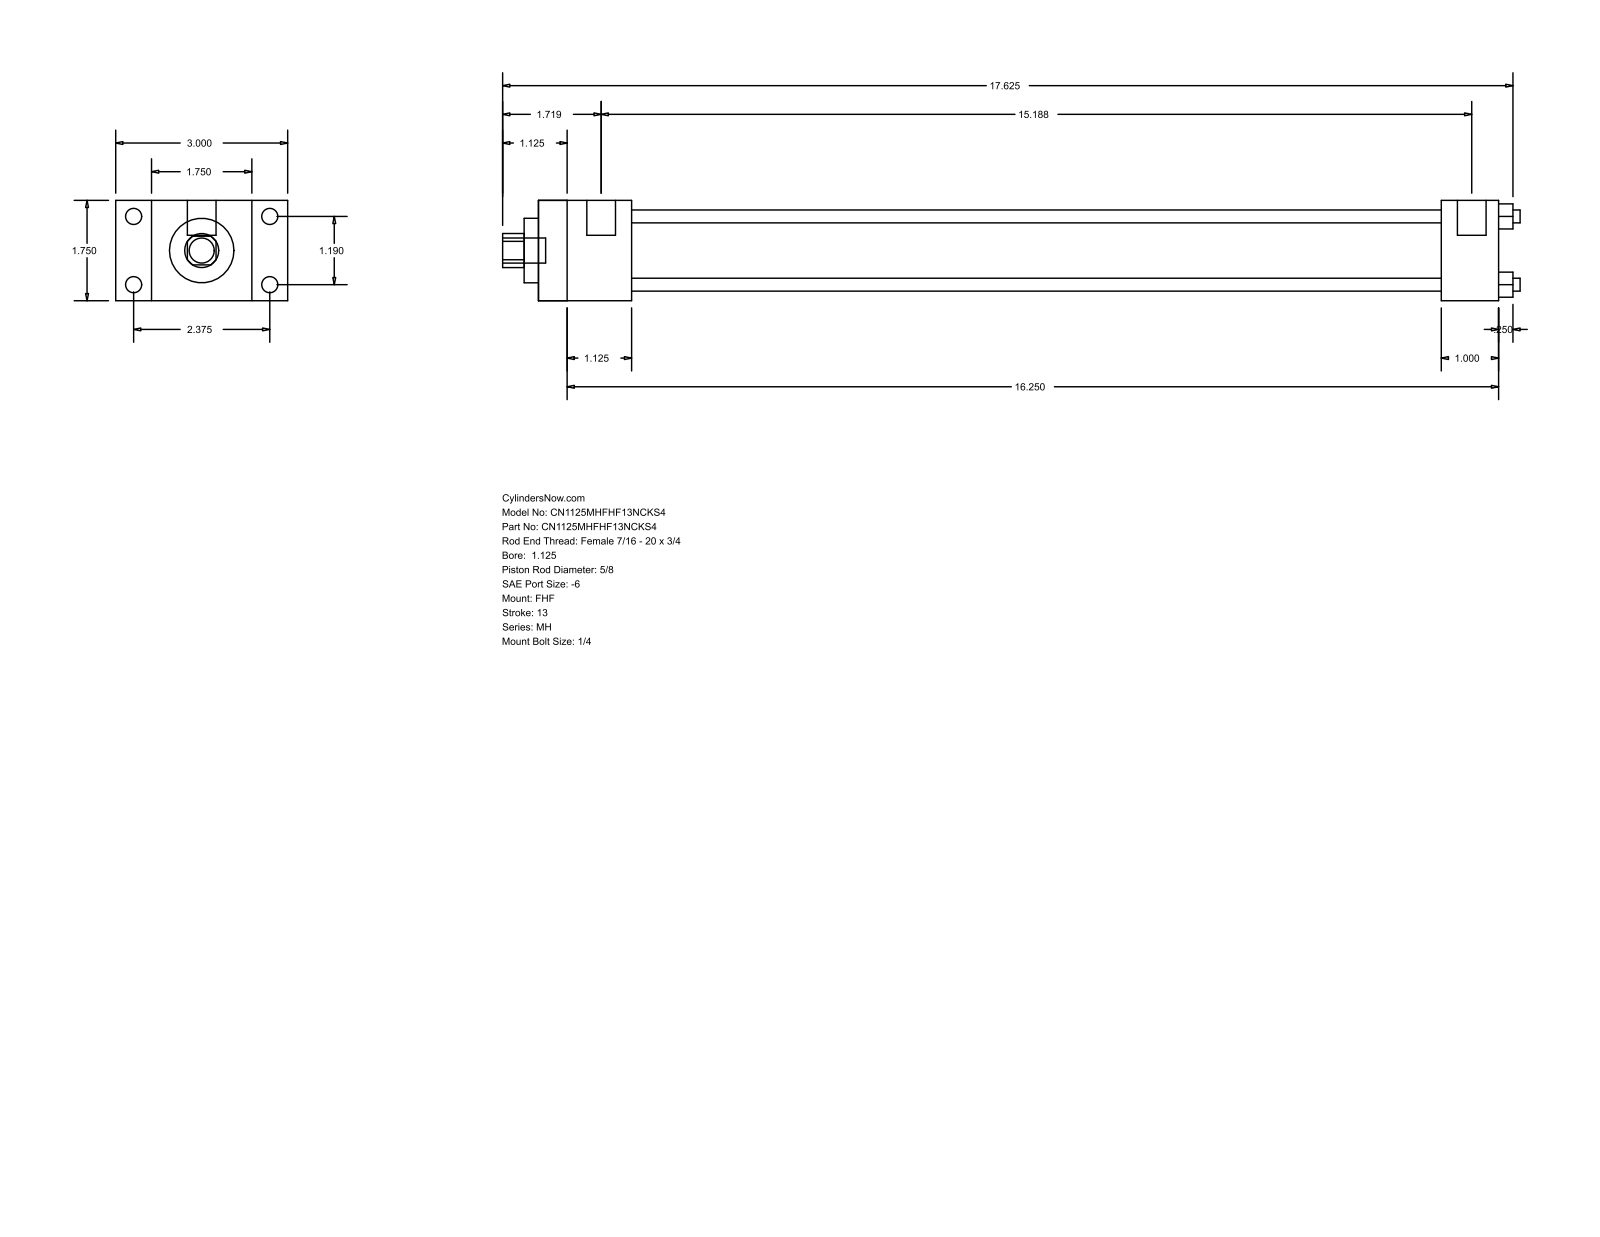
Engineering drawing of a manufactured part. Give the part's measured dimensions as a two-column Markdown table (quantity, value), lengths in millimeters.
| quantity | value |
| --- | --- |
| part name | MH_FHF__0112_0.625 |
| STEP written by | GSSL Pune (CONFIG_CONTROL_DESIGN) |
| units | millimeters |
| bodies | 0 solids, 88 faces (60 planar, 28 cylindrical, 0 other) |
| overall size | 450.85 × 76.2 × 44.45 |
| round holes (diameter × count) | 5.71 × 4, 15.88 × 1, 28.57 × 1, 34.92 × 1 |
| round bosses / shafts (diameter × count) | 7.14 × 4, 5.56 × 4, 12.7 × 2, 11.11 × 1 |
| partial cylindrical surfaces (radius × count) | 7.54 × 1 |
| main face-to-face distances | 44.46, 15.87, 60.33, 41.27, 76.2, 425.44, 384.17, 400.05, 358.78, 25.39 |
| hole center spacings | 21.37, 30.22, 42.74 |
